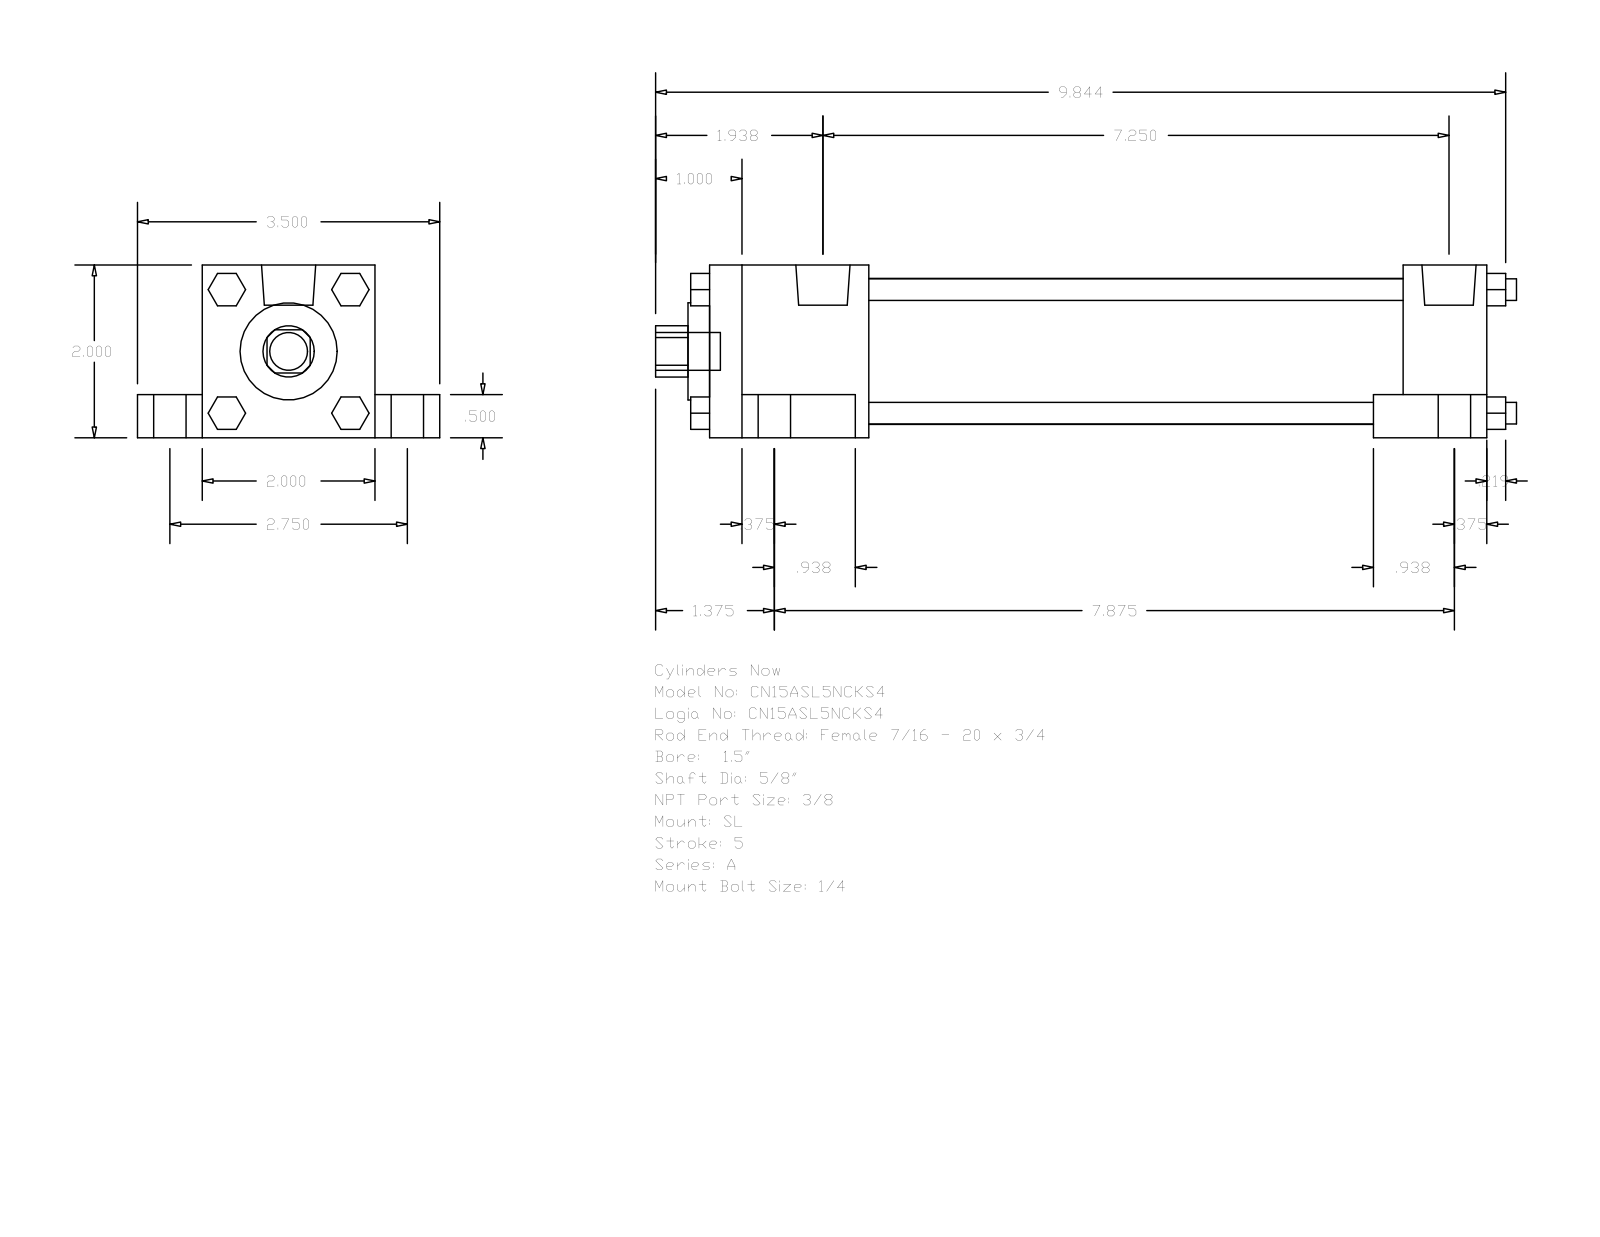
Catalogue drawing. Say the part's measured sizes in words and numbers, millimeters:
The part is named "A_SL__0150_0.625". Its 3-D file was written by "GSSL Pune (CONFIG_CONTROL_DESIGN)". It is 0 solids with 148 faces: 112 planar, 36 cylindrical and 0 other. Overall it measures 253.21 by 88.9 by 50.8 millimeters. Round holes: 1 of diameter 15.88, 1 of diameter 28.57, 1 of diameter 42.93. Round bosses or shafts: 4 of diameter 15.88, 4 of diameter 9.53, 4 of diameter 6.35, 4 of diameter 5.56, 2 of diameter 15.93, 1 of diameter 11.11. Partial cylindrical surfaces (rounded edges, fillets, slot ends): 1 of radius 7.54. The main face-to-face distances are 50.8, 19.05, 12.7, 38.1, 69.85, 228.59, 9.52, 203.99, 24.6, 46.83.
